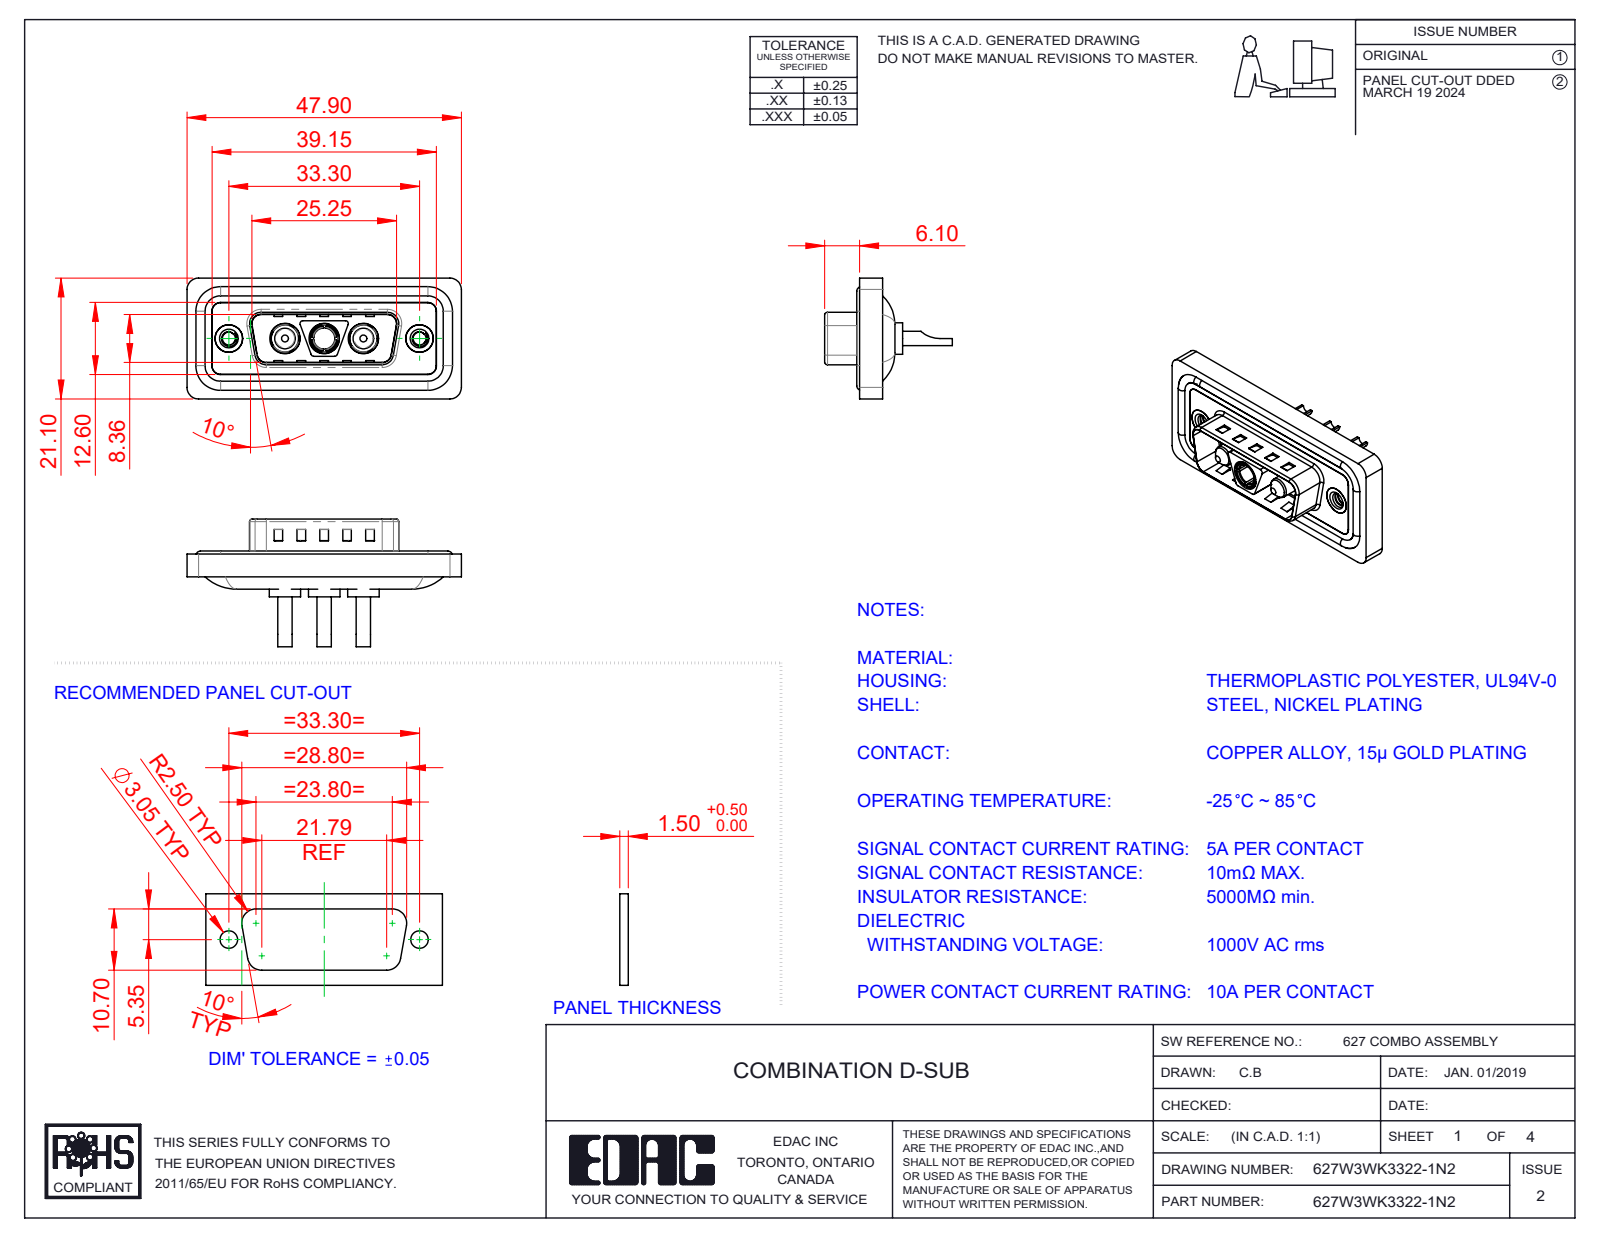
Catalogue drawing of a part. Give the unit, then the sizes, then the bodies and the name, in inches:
Units: inches
Overall size (bounding box): 1.886 × 0.878 × 0.831
Round holes (diameter × count): ⌀0.067 ×3, ⌀0.191 ×3, ⌀0.209 ×3, ⌀0.089 ×2, ⌀0.157 ×2, ⌀0.189 ×2, ⌀0.197 ×2, ⌀0.146 ×1
Round bosses / shafts (diameter × count): ⌀0.063 ×4, ⌀0.217 ×3, ⌀0.205 ×3, ⌀0.187 ×3, ⌀0.148 ×3, ⌀0.098 ×3, ⌀0.193 ×2, ⌀0.142 ×2
Partial cylindrical surfaces — rounded edges, fillets, slot ends (radius × count): R0.059 ×26, R0.079 ×20, R0.02 ×12, R0.063 ×8, R0.01 ×4, R0.024 ×4, R0.026 ×4, R0.035 ×4
Main face-to-face distances: 0.016, 0.043, 0.059, 0.02, 0.063, 0.122, 0.114, 0.157, 0.032, 0.377
Hole centre spacings: 0.27, 0.386, 0.656, 0.925, 0.539, 1.311
Volume: 0.347 in³ · Surface area: 14.37 in²
Bodies: 13 solids, 627 faces (237 planar, 259 cylindrical, 131 other)
Part name (STEP PRODUCT): Power Socket_10A SC; 627Combo Housing_3WK3; Power Pin_10A SC; 627Combo Shell Front_15 Contacts (+4 more)
STEP written by: SolidWorks 2023 (CONFIG_CONTROL_DESIGN)
